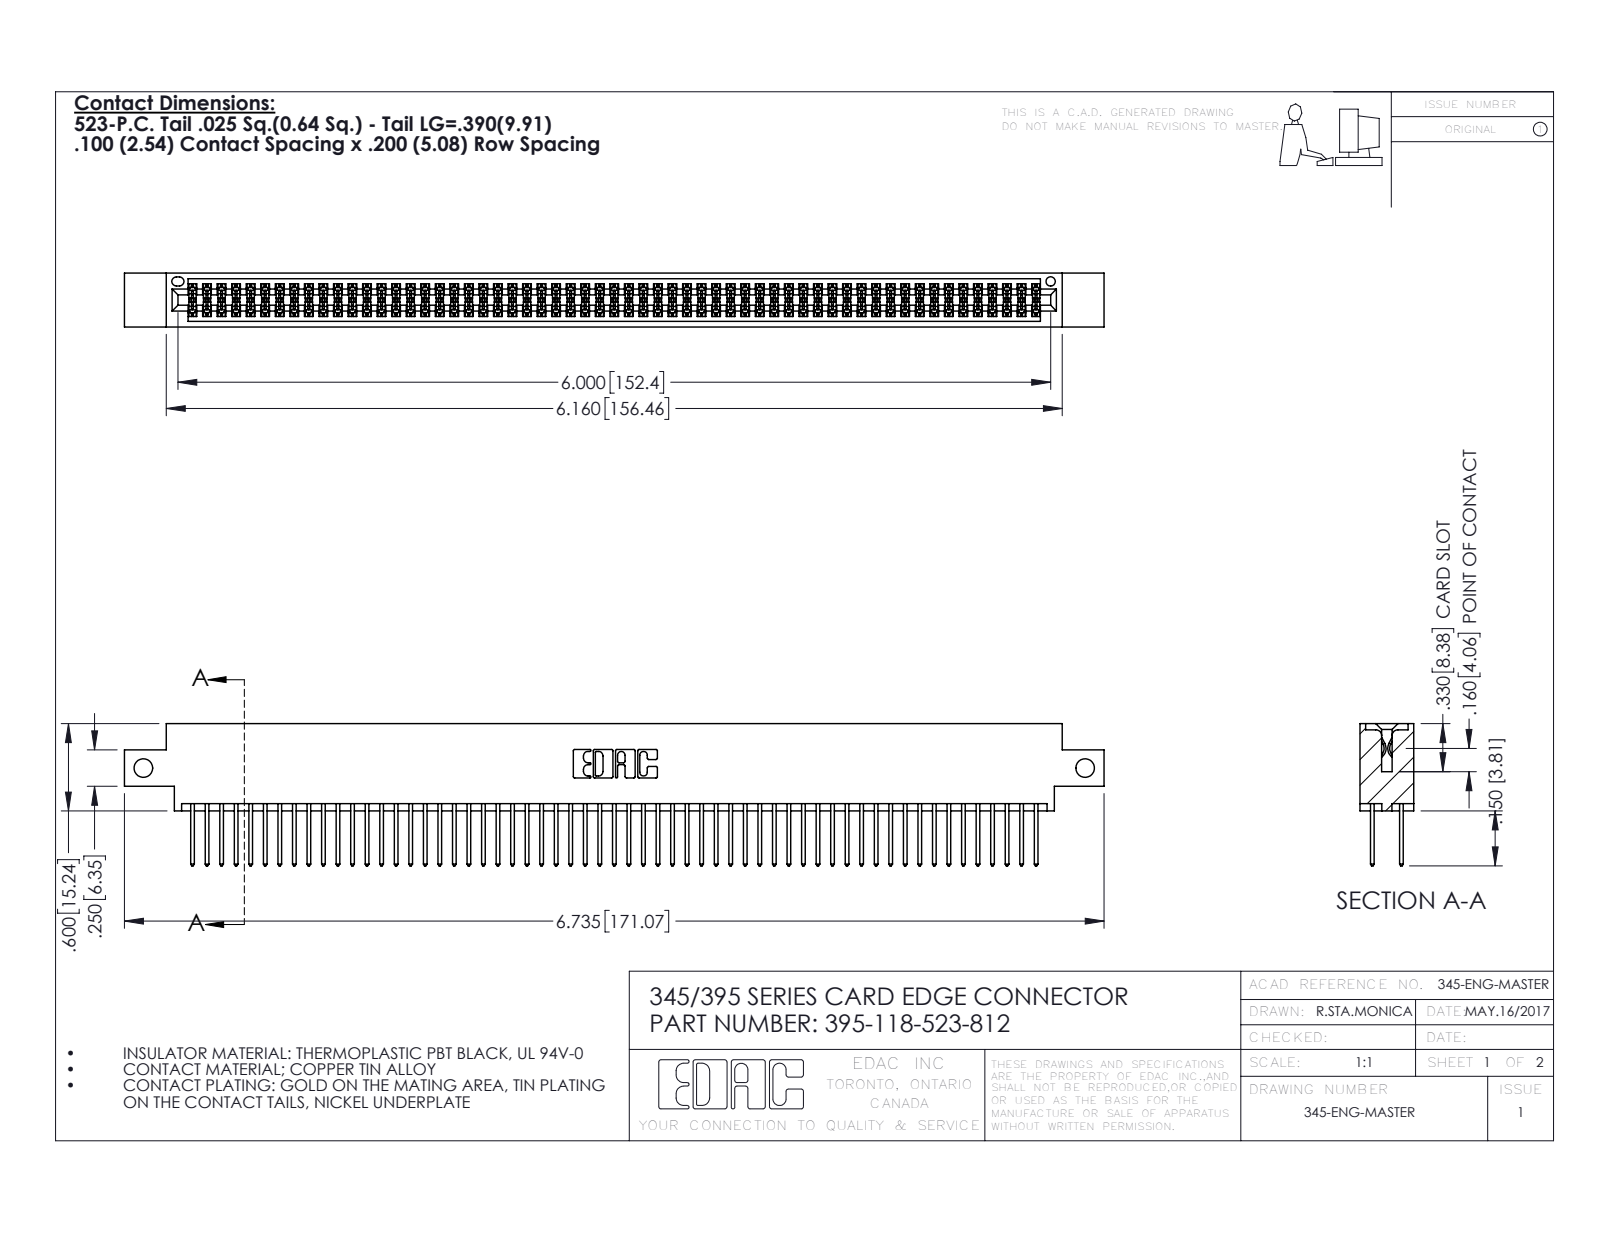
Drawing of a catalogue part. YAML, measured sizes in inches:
part_name: "345-292-001_345-293-123; 395-118-523-812; 345 Part_0.170 Offset - Side Mount"
step_written_by: "SolidWorks 2016 (CONFIG_CONTROL_DESIGN)"
units: inches
bodies: {solids: 119, faces: 6030, planar: 3978, cylindrical: 2052, other: 0}
overall_size: [6.735, 0.977, 0.37]
volume: 1.026
surface_area: 40.73
round_holes:
  - {diameter: 0.128, count: 2}
  - {diameter: 0.064, count: 1}
partial_cylinders:
  - {radius: 0.006, count: 177}
  - {radius: 0.01, count: 118}
  - {radius: 0.01, count: 22}
  - {radius: 0.007, count: 6}
  - {radius: 0.031, count: 6}
  - {radius: 0.026, count: 3}
  - {radius: 0.014, count: 2}
  - {radius: 0.019, count: 2}
face_to_face_distances: [0.298, 0.072, 0.2, 0.098, 0.272, 0.025, 0.37, 0.225, 0.175, 0.149]
hole_center_spacings: [6.475]
